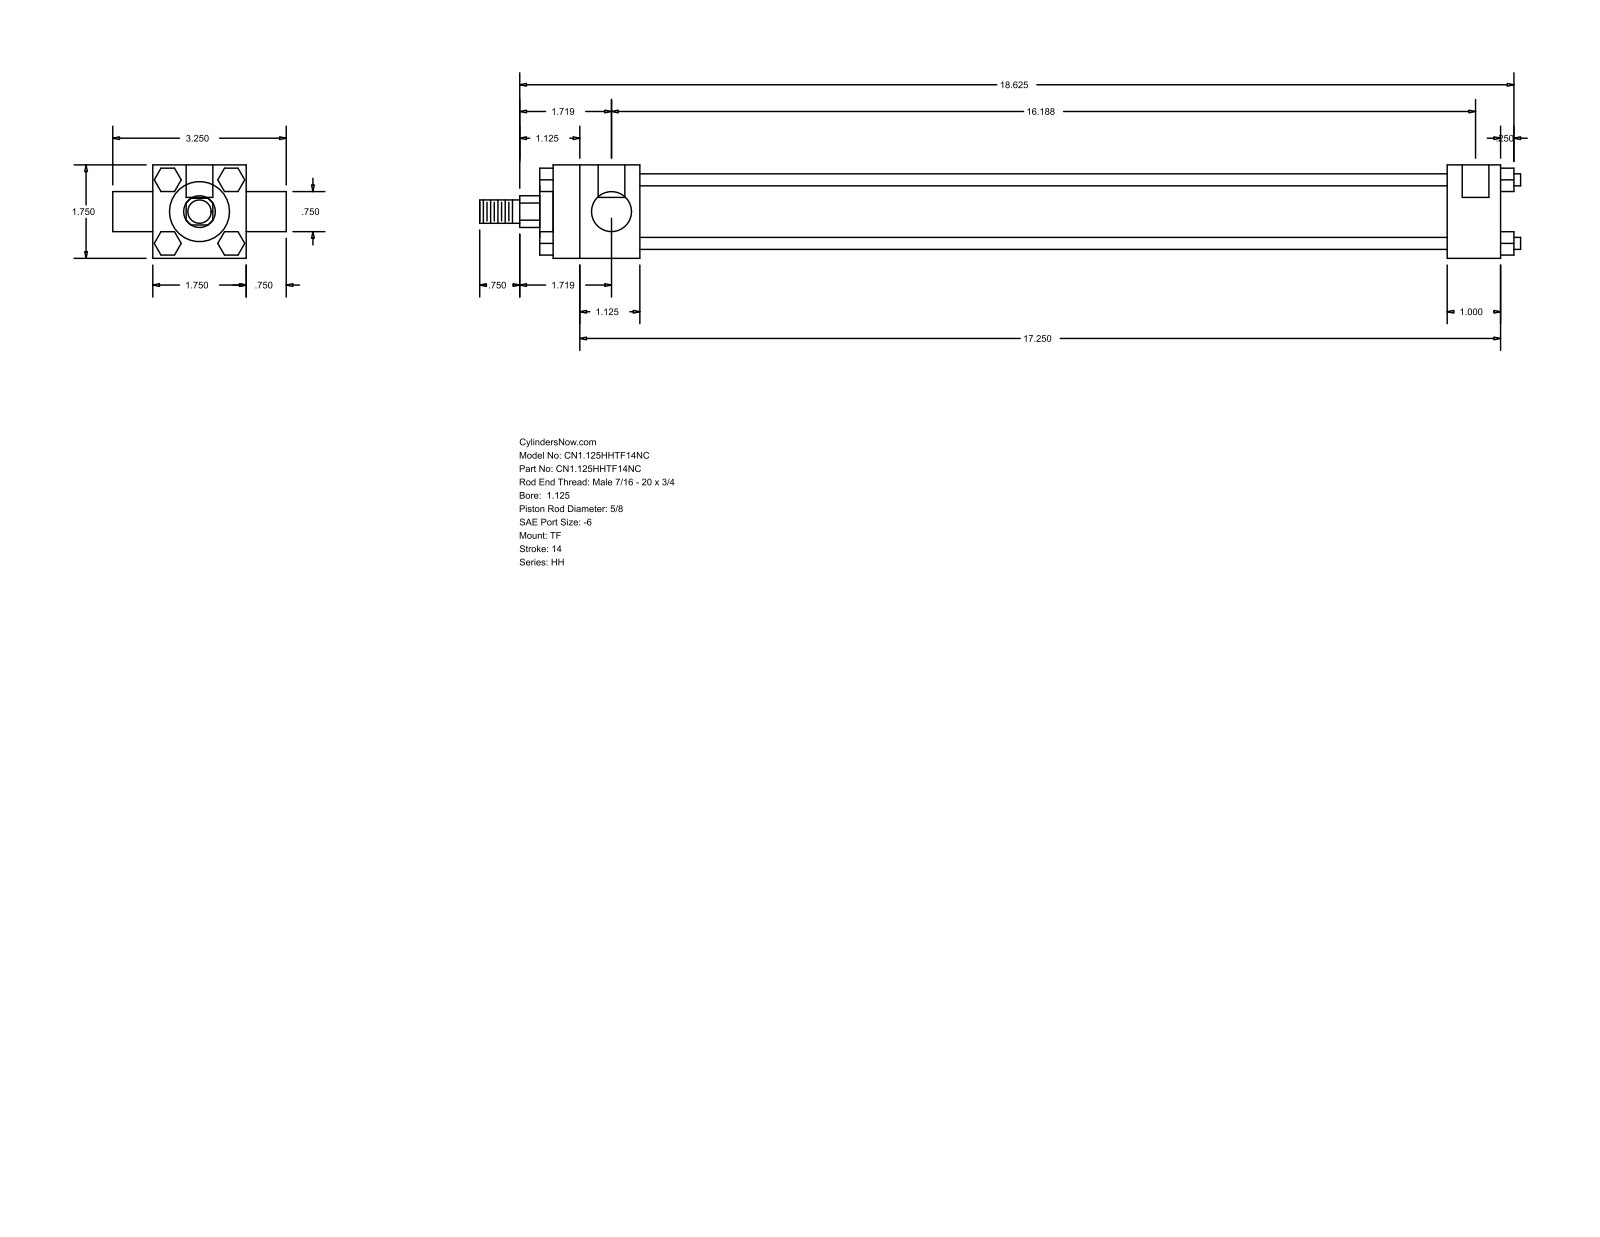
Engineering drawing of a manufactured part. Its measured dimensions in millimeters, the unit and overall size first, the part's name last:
Units: millimetres
Overall size (bounding box): 495.3 × 82.55 × 44.45
Round holes (diameter × count): ⌀5.56 ×3, ⌀12.7 ×2
Round bosses / shafts (diameter × count): ⌀5.71 ×4, ⌀34.92 ×1, ⌀28.57 ×1, ⌀19.05 ×1, ⌀15.88 ×1, ⌀11.11 ×1
Partial cylindrical surfaces — rounded edges, fillets, slot ends (radius × count): R7.54 ×1
Main face-to-face distances: 44.46, 11.11, 384.17, 409.58, 25.41, 41.27, 425.44, 450.85, 47.62, 6.35
Hole centre spacings: 3.17, 407.99, 411.16
Bodies: 0 solids, 120 faces (92 planar, 28 cylindrical, 0 other)
Part name (STEP PRODUCT): HH_TF__0112_0.625
STEP written by: GSSL Pune (CONFIG_CONTROL_DESIGN)
